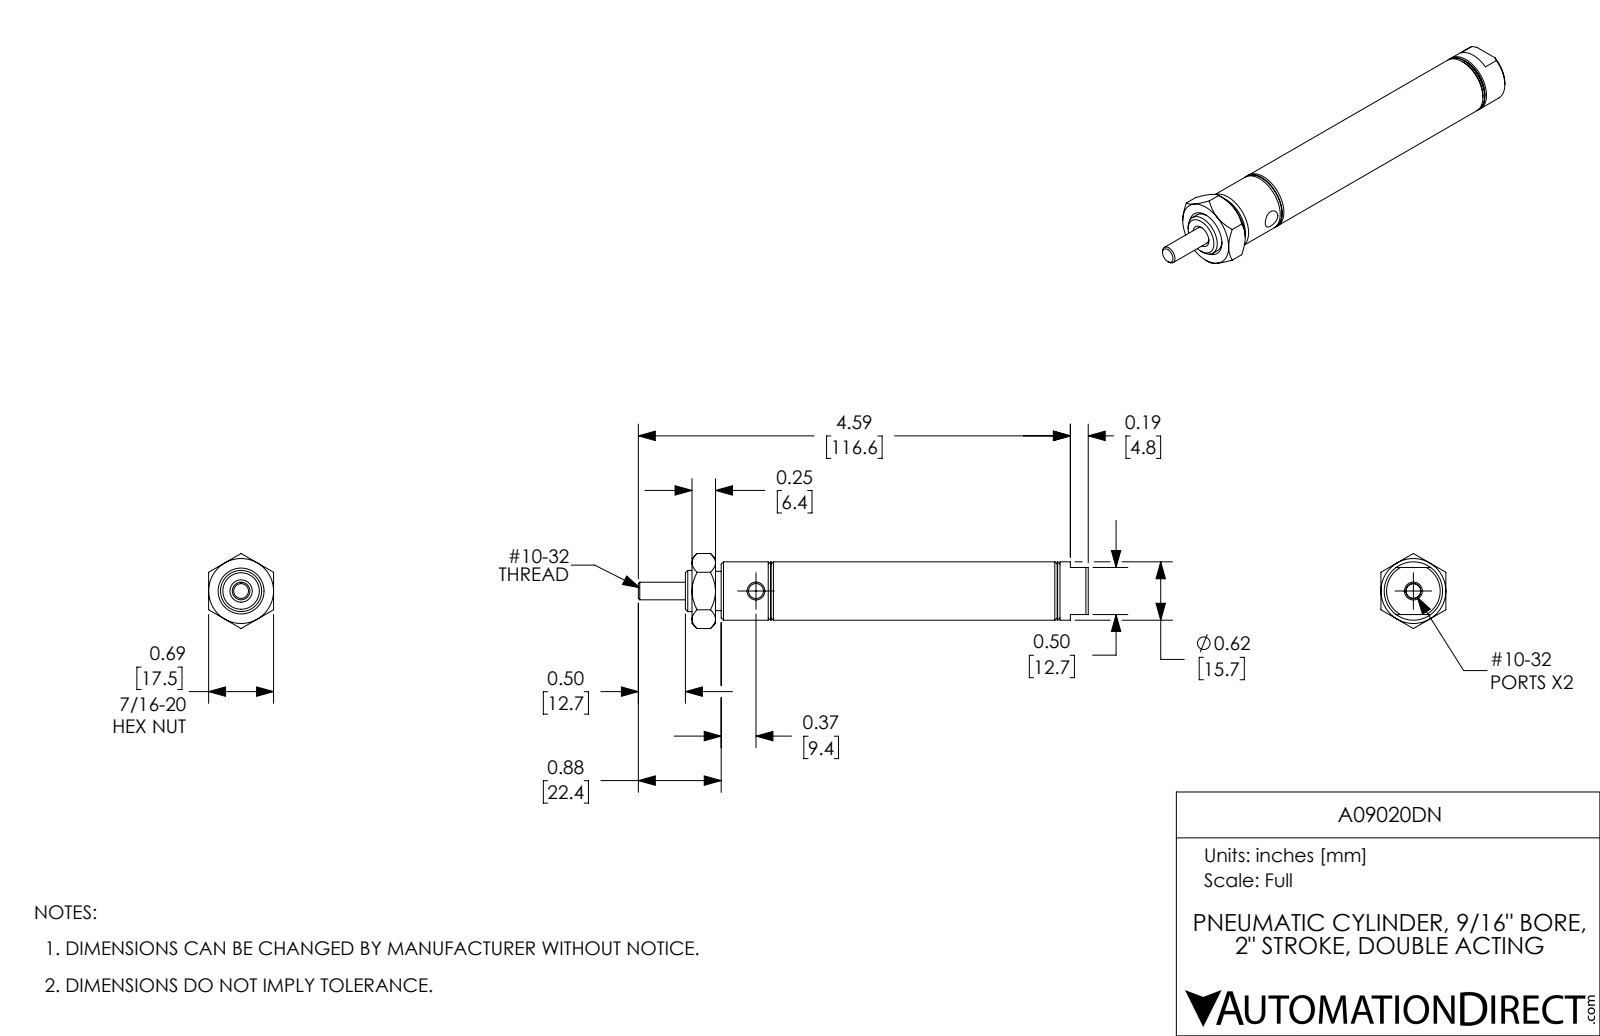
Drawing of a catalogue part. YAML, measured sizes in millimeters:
part_name: "A09020DN; A09020DN_Mounting Nut_D-154; A09020DN-Rod; A09020DN-MainBody"
step_written_by: "SolidWorks 2017 (AUTOMOTIVE_DESIGN)"
units: millimeters
bodies: {solids: 3, faces: 100, planar: 28, cylindrical: 34, other: 38}
overall_size: [121.4, 20.2, 17.5]
volume: 13700
surface_area: 12670
round_holes:
  - {diameter: 4, count: 2}
  - {diameter: 4.8, count: 2}
  - {diameter: 4, count: 1}
  - {diameter: 4.7, count: 1}
  - {diameter: 11.1, count: 1}
  - {diameter: 14.3, count: 1}
round_bosses_or_shafts:
  - {diameter: 15.7, count: 1}
  - {diameter: 10.6, count: 1}
face_to_face_distances: [17.8, 81.3, 12.7, 17.5, 63.5, 100.6, 82.8, 19.3, 30.5, 50.8]
